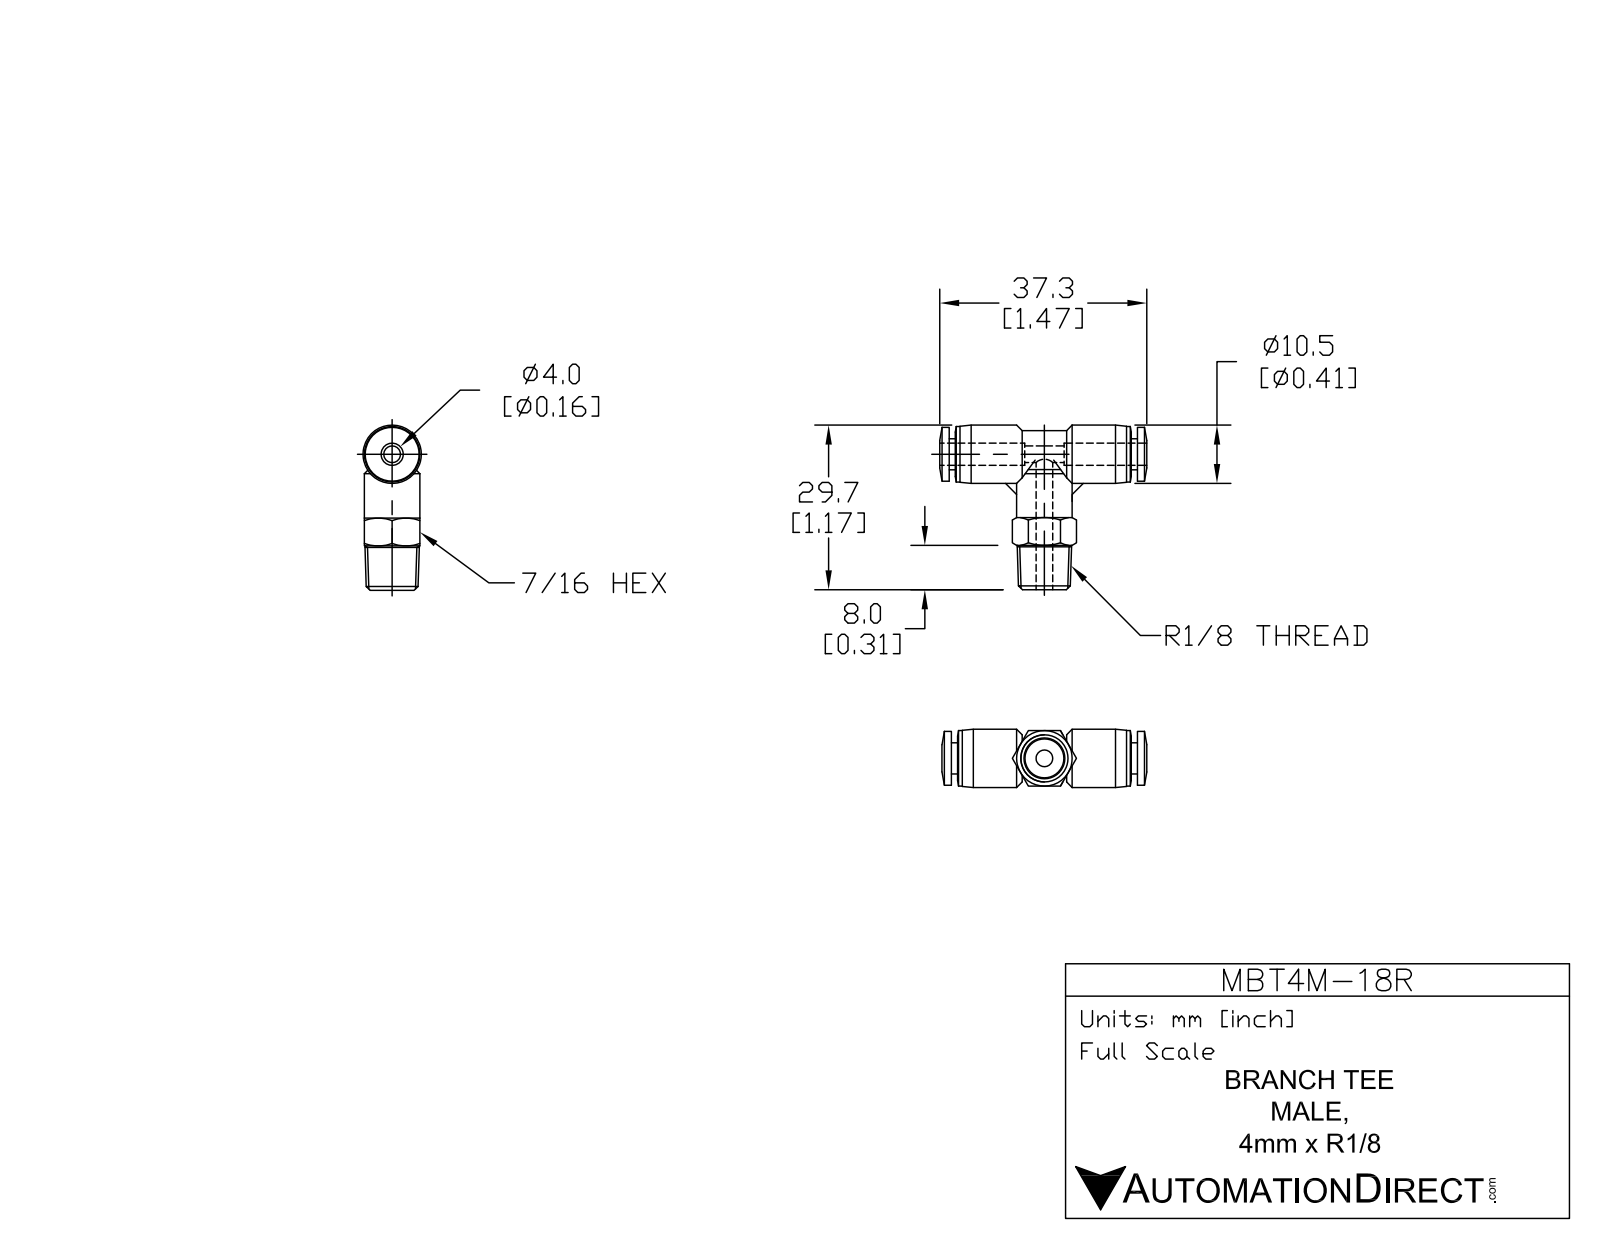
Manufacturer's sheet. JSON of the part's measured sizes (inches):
{"part_name": "MBT4M-18R", "step_written_by": "SolidWorks 2015 (AUTOMOTIVE_DESIGN)", "units": "inches", "bodies": {"solids": 1, "faces": 99, "planar": 24, "cylindrical": 33, "other": 42}, "overall_size": [1.453, 1.171, 0.413], "volume_in3": 0.221, "surface_area_in2": 4.342, "round_holes": [[0.118, 2], [0.169, 1]], "round_bosses_or_shafts": [[0.394, 2], [0.413, 1], [0.382, 1], [0.315, 1], [0.22, 1]], "partial_cylinders_radius": [[0.157, 1]], "face_to_face_distances": [0.394, 0.043, 1.276, 1.319, 1.232, 0.516, 0.803, 0.472, 0.76, 0.157]}
